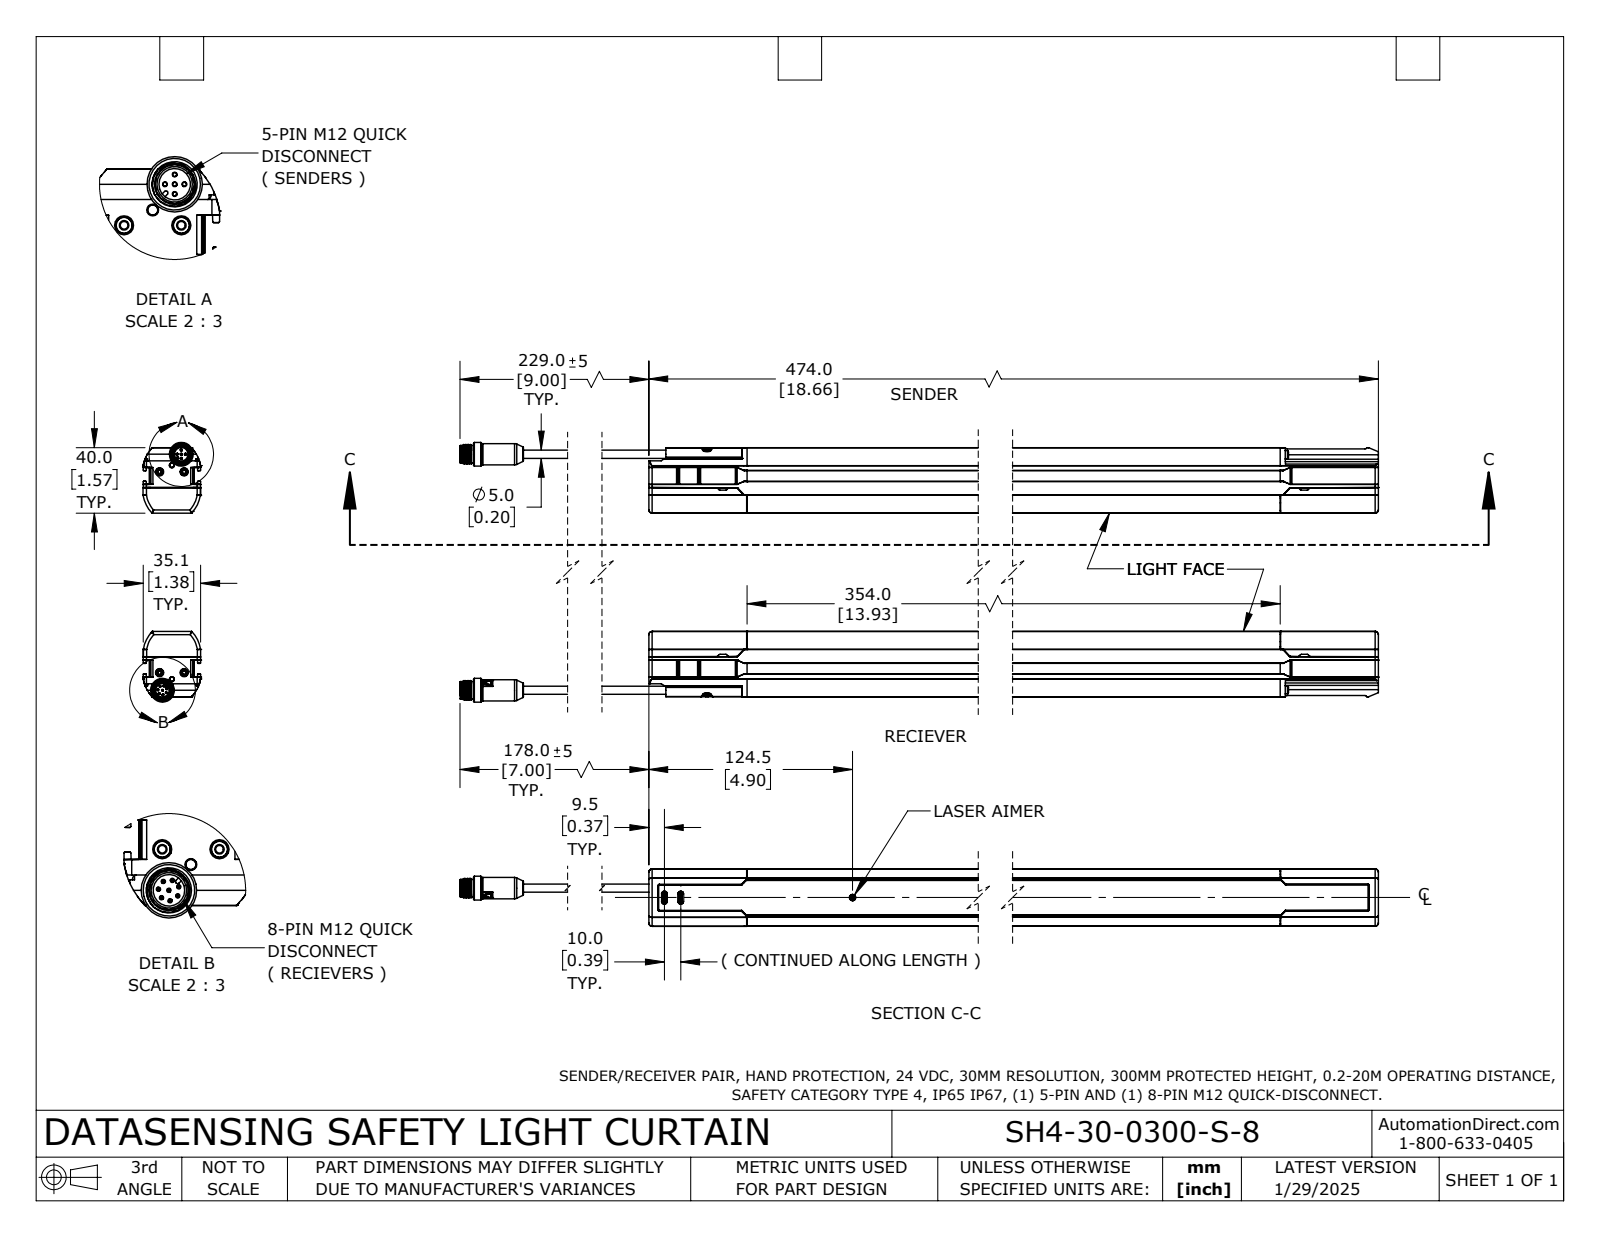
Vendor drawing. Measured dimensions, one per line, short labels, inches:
name: 957920057
written by: SolidWorks 2024 (AUTOMOTIVE_DESIGN)
unit: in
bodies: 4 solids, 2608 faces (1186 planar, 784 cylindrical, 638 other)
size: 21.154 × 6.248 × 1.384
volume: 42.67 in³; area: 266.9 in²
holes: 6× ⌀0.079, 6× ⌀0.118, 6× ⌀0.197, 2× ⌀0.101, 2× ⌀0.102, 2× ⌀0.102, 2× ⌀0.103, 2× ⌀0.325, 2× ⌀0.382, 2× ⌀0.407, 2× ⌀0.425, 1× ⌀0.11
bosses: 10× ⌀0.197, 8× ⌀0.087, 8× ⌀0.031, 6× ⌀0.172, 5× ⌀0.039, 4× ⌀0.217, 2× ⌀0.571, 2× ⌀0.512
rounds: 174× R0.01, 74× R0.016, 50× R0.02, 36× R0.008, 26× R0.031, 16× R0.047, 14× R0.079, 12× R0.031
face distances: 1.496, 4.496, 3, 0.079, 1.033, 0.083, 1.417, 4.575, 3.079, 1.413
hole spacings: 0.591, 0.866, 0.43, 0.433, 0.434, 0.017, 0.429, 0.43
